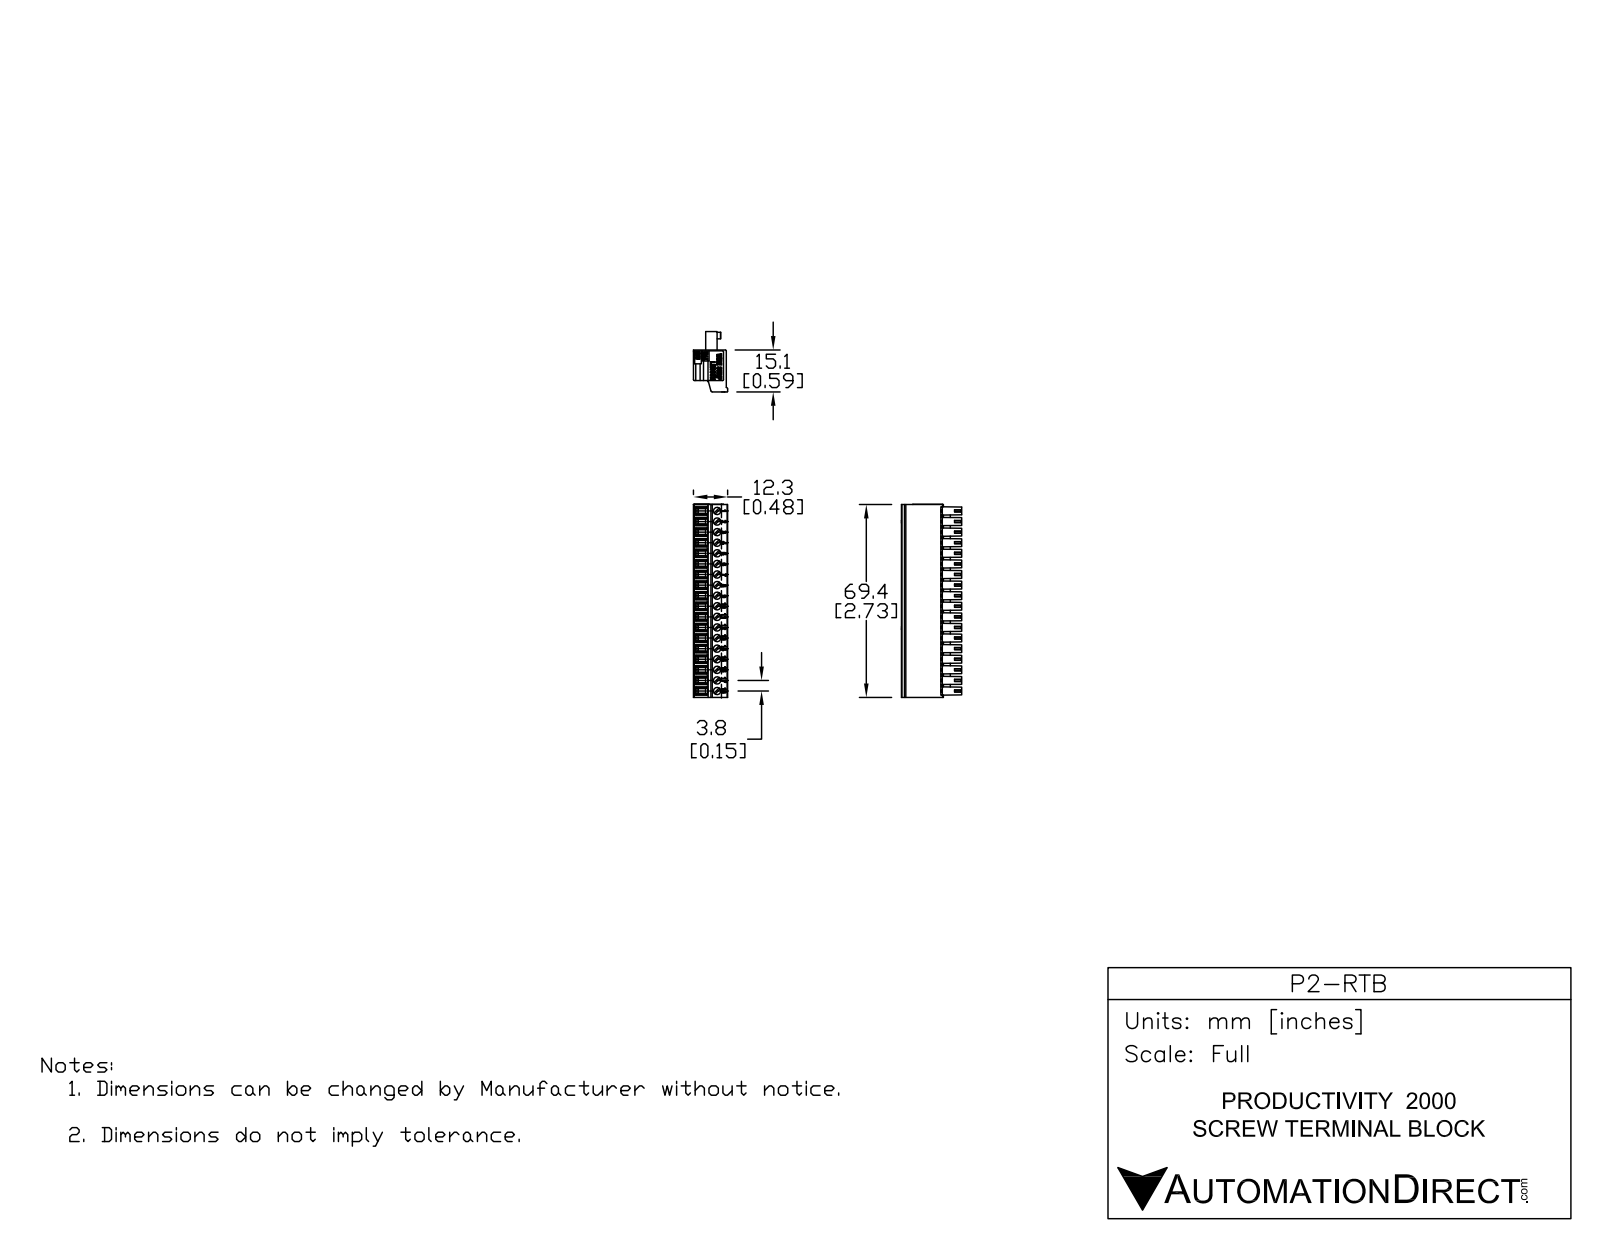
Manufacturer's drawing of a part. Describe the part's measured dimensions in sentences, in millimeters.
The part is named "P2-RTB c". Its 3-D file was written by "SolidWorks 2017 (AUTOMOTIVE_DESIGN)". It is 1 solid with 1541 faces: 624 planar, 507 cylindrical and 410 other. Overall it measures 69.37 by 21.71 by 11.8 millimeters. Its volume is 11 061 cubic millimeters and its surface area 7 370 square millimeters. Round holes: 18 of diameter 1.6, 18 of diameter 2.6. Partial cylindrical surfaces (rounded edges, fillets, slot ends): 257 of radius 0.1, 36 of radius 0.3, 18 of radius 1.83, 2 of radius 0.3, 1 of radius 0.5. The main face-to-face distances are 3.81, 7.62, 11.43, 11.8, 15.24, 19.05, 22.86, 26.67, 30.48, 34.29. The hole center spacings are 3.81, 7.62, 4.26, 11.43, 7.85, 15.24, 11.59, 15.36.
